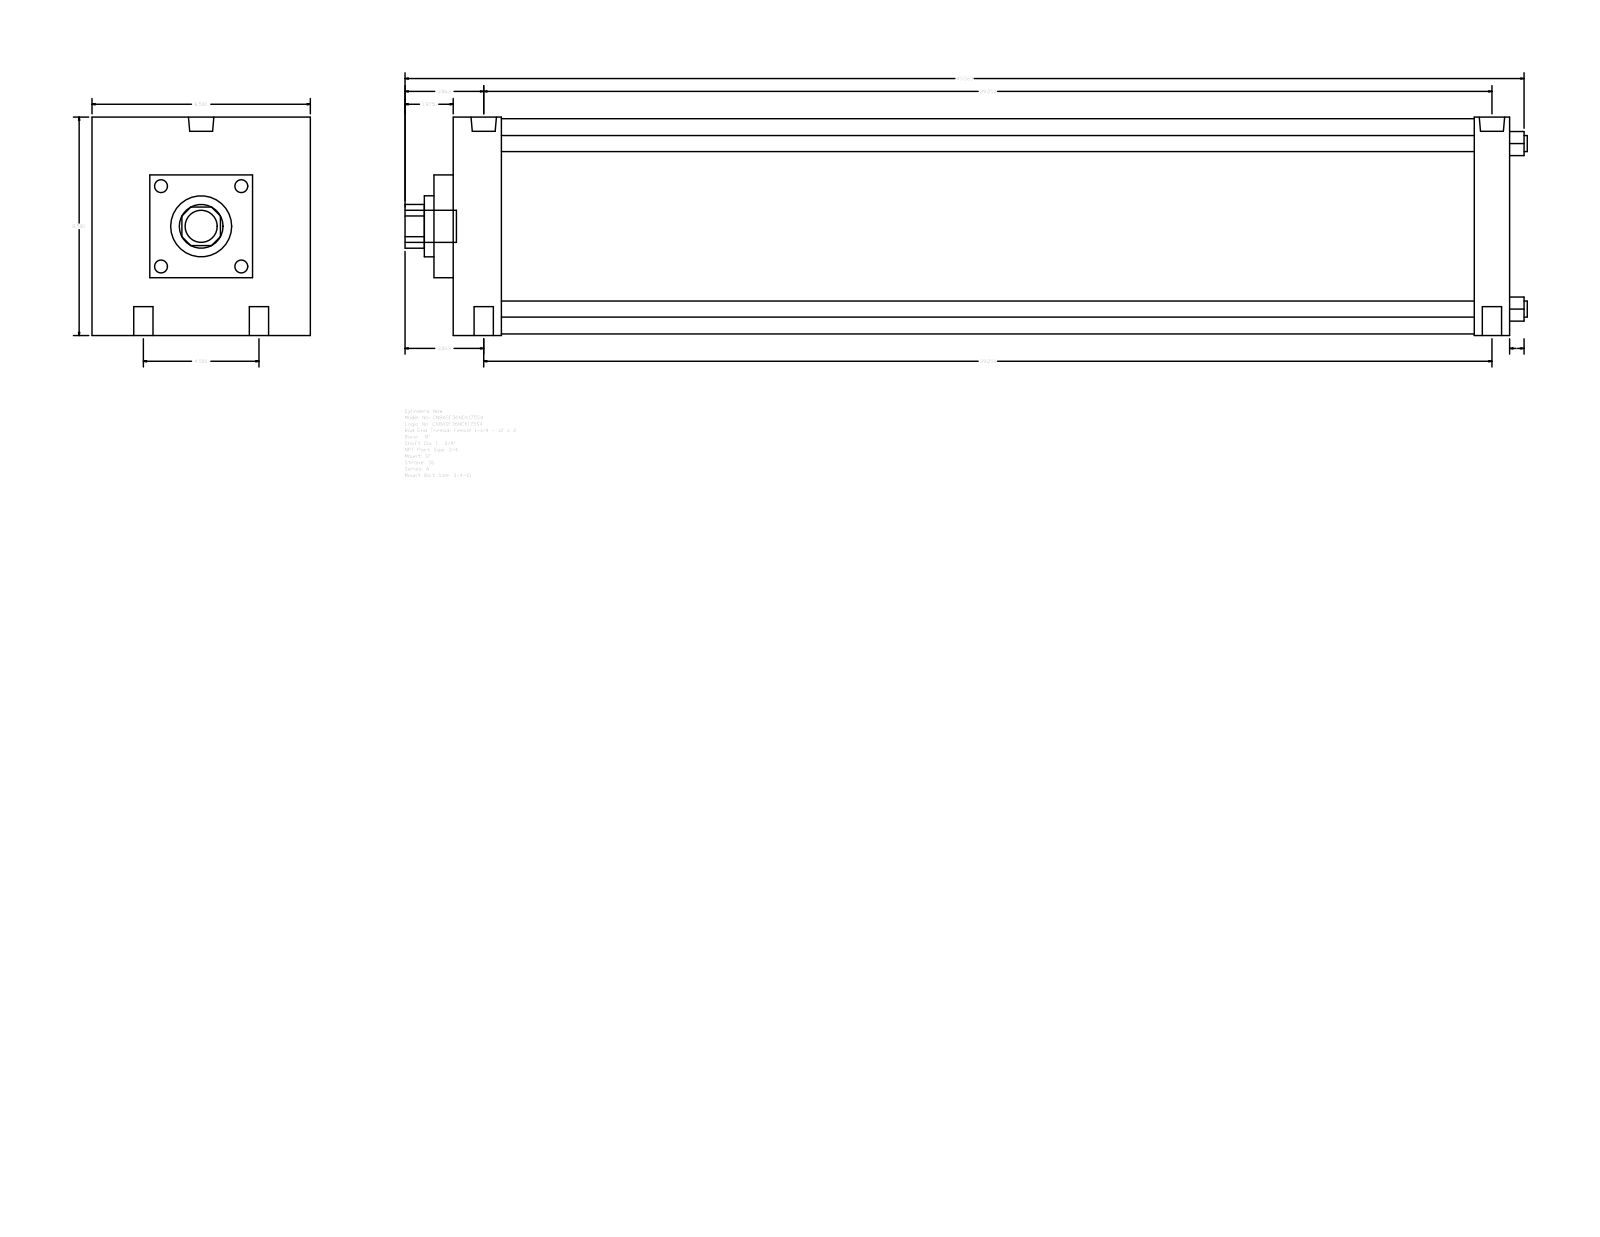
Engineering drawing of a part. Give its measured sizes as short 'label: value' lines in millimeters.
name: A_SF__0800_1.75
written by: GSSL Pune (CONFIG_CONTROL_DESIGN)
unit: mm
bodies: 0 solids, 93 faces (67 planar, 26 cylindrical, 0 other)
size: 1109.66 × 215.9 × 215.9
holes: 4× ⌀19.05, 2× ⌀15.08, 2× ⌀25.12, 1× ⌀44.45, 1× ⌀60.33
bosses: 4× ⌀15.88, 1× ⌀212.72, 1× ⌀31.75
rounds: 1× R21.63
face distances: 1044.58, 215.9, 34.92, 47.63, 1009.66, 962.03, 996.95, 19.05, 158.75, 57.15
hole spacings: 57.15, 998.59, 996.95, 114.3, 1003.48, 984.25
